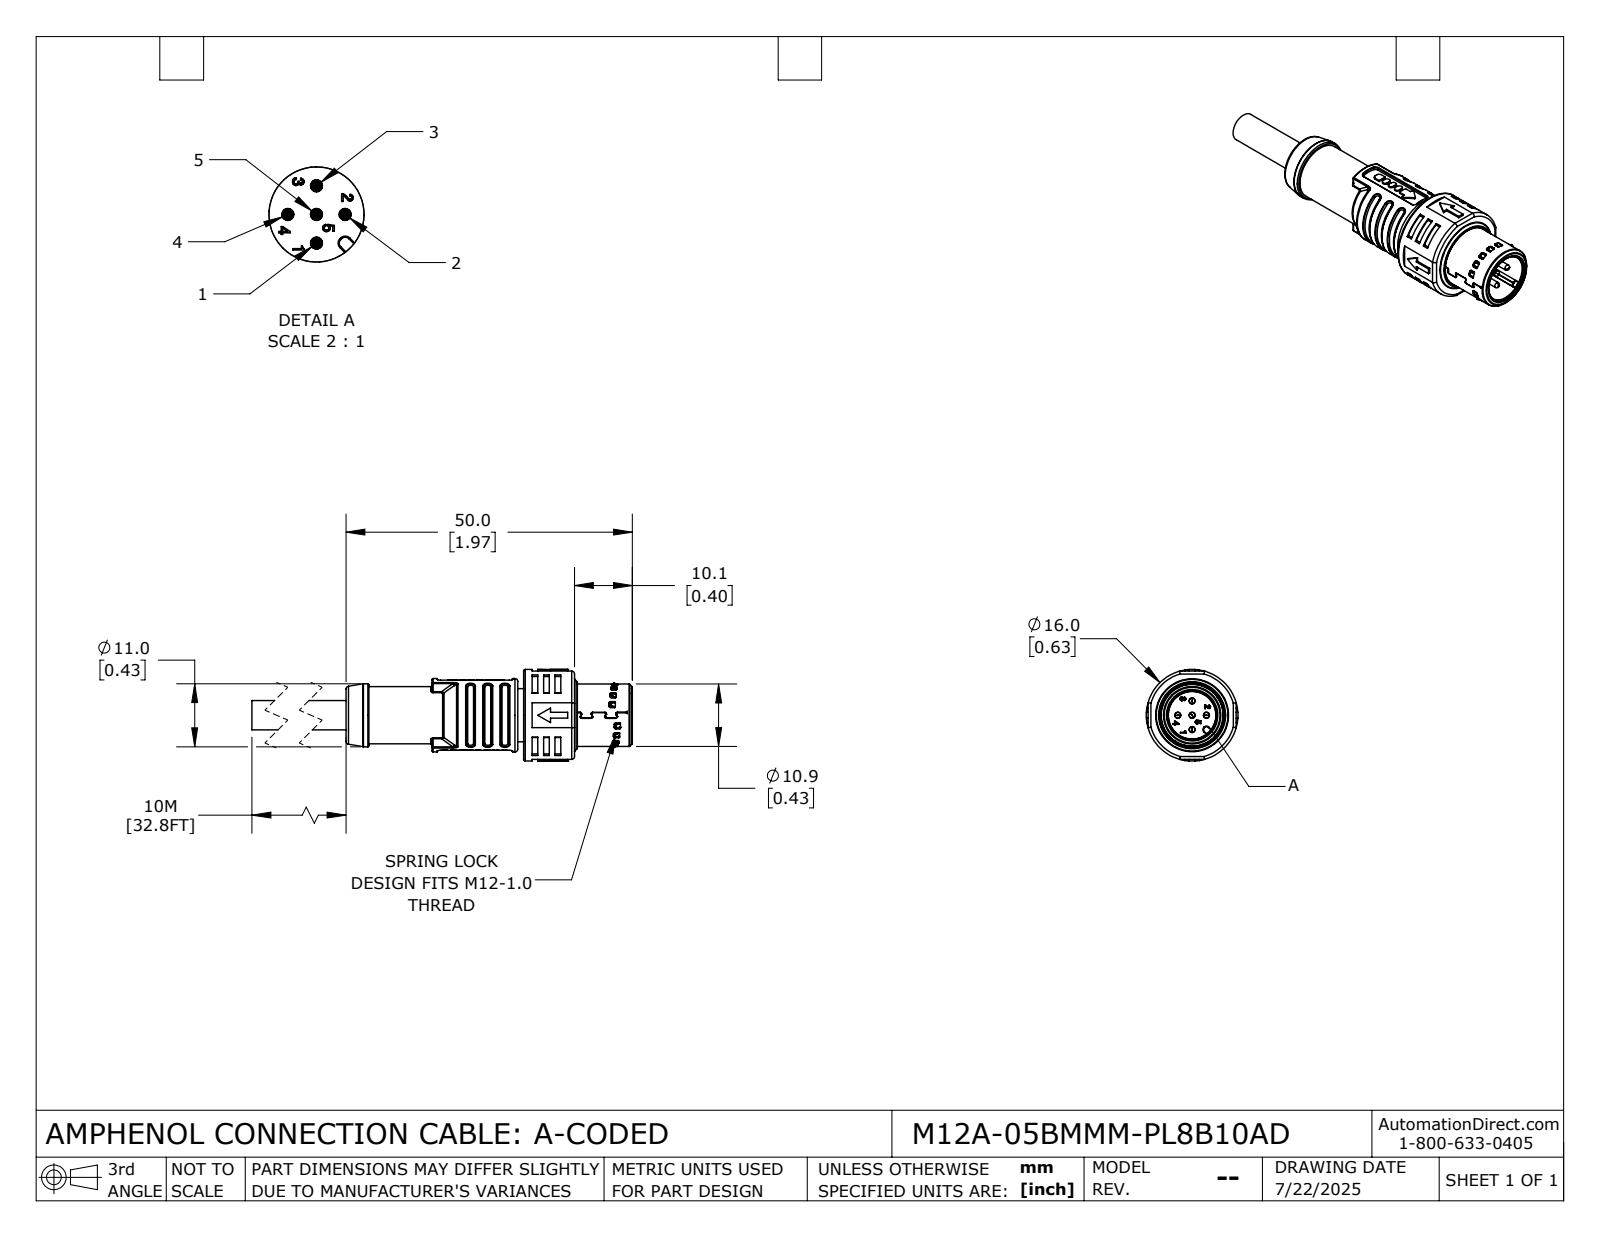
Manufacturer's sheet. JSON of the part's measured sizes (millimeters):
{"part_name": "M12A-05BMMM-PL8B10AD", "step_written_by": "SolidWorks 2024 (CONFIG_CONTROL_DESIGN)", "units": "millimeters", "bodies": {"solids": 1, "faces": 2230, "planar": 1085, "cylindrical": 648, "other": 497}, "overall_size": [65, 16, 16], "volume_mm3": 5076, "surface_area_mm2": 5586, "round_holes": [[1.05, 5], [8.3, 1], [9, 1], [10.15, 1], [10.5, 1], [10.9, 1], [11.5, 1], [11.8, 1], [14.2, 1]], "round_bosses_or_shafts": [[1, 5], [16, 1], [14.1, 1], [12.8, 1], [12.4, 1], [11, 1], [10.45, 1], [10.4, 1]], "partial_cylinders_radius": [[0.2, 114], [0.25, 66], [0.3, 64], [0.15, 44], [0.5, 38], [0.13, 12], [0.7, 11], [0.1, 10]], "face_to_face_distances": [1, 10.1, 8.9, 8.6, 2.5, 30, 1.5, 1.2, 32.5, 15.4], "hole_center_spacings": [2.5, 3.54, 5]}
